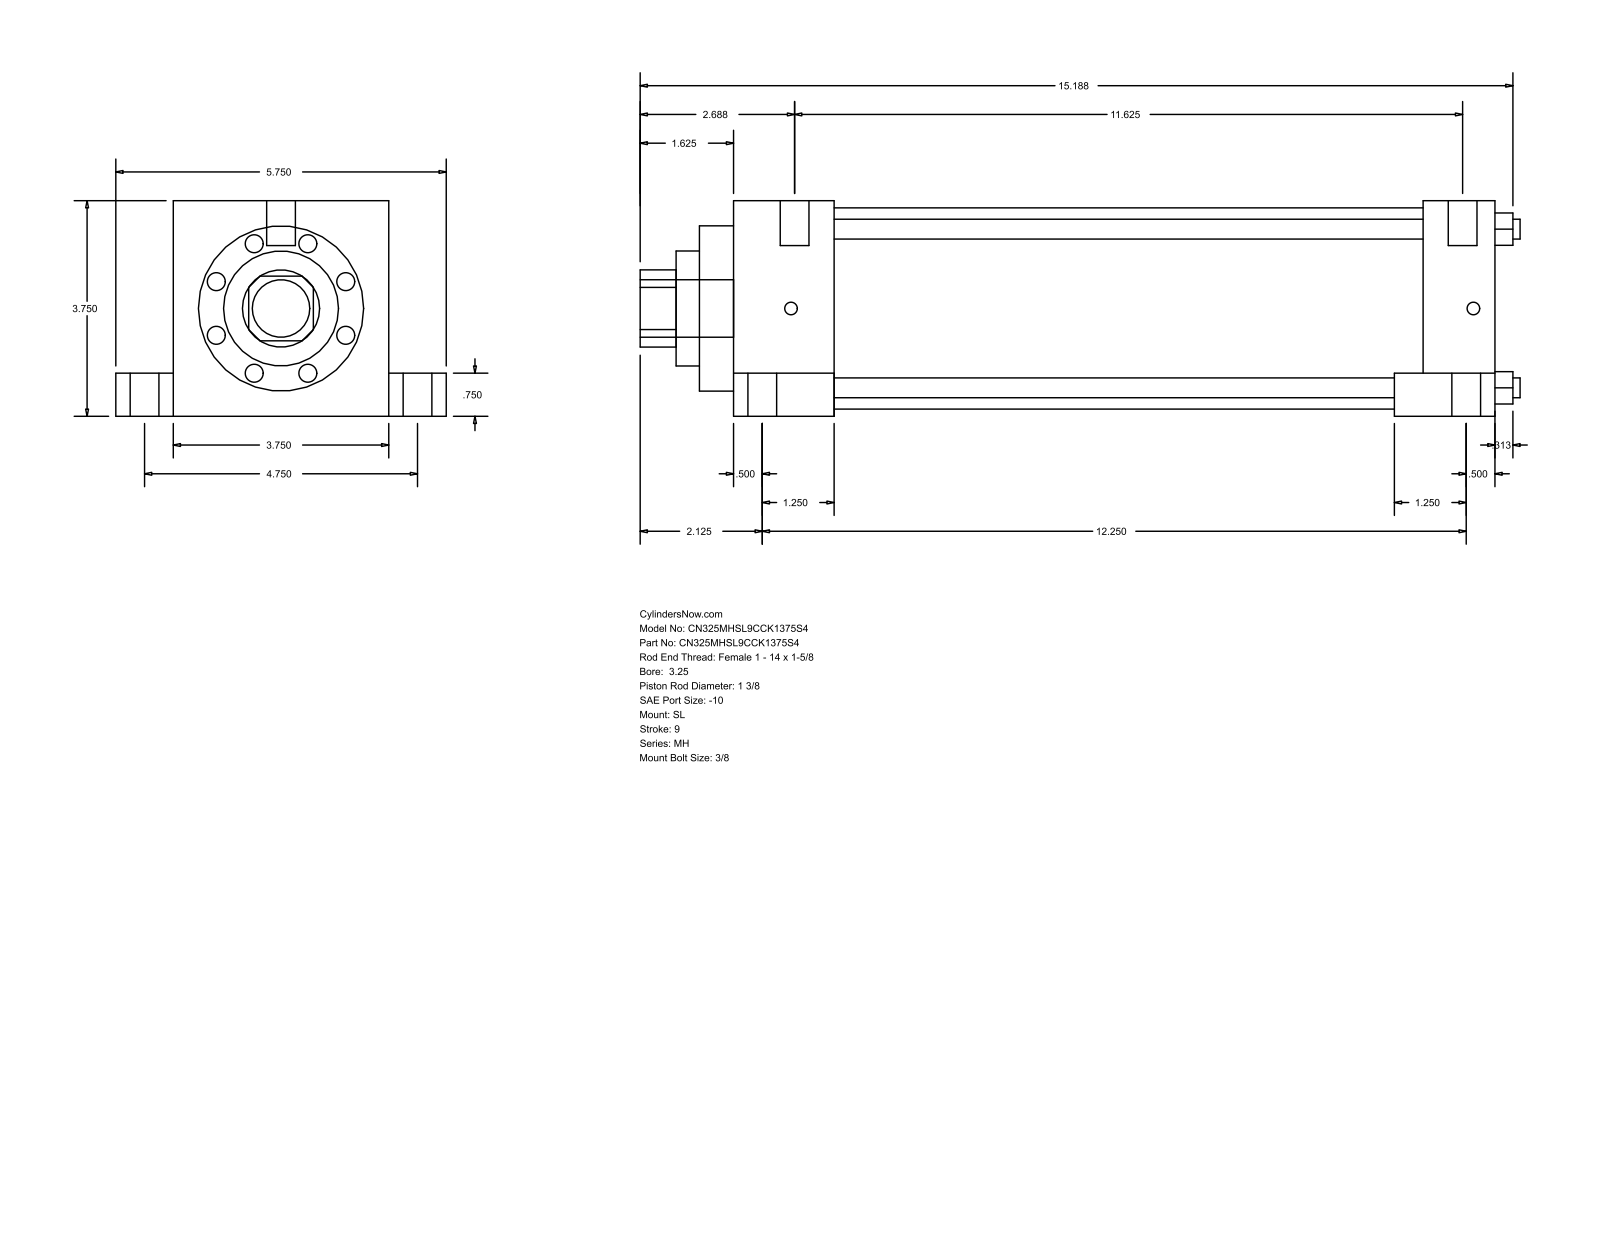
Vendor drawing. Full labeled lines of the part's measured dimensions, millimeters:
Part name (STEP PRODUCT): MH_SL__0325_1.375
STEP written by: GSSL Pune (CONFIG_CONTROL_DESIGN)
Units: millimetres
Bodies: 0 solids, 110 faces (77 planar, 33 cylindrical, 0 other)
Overall size (bounding box): 388.94 × 146.05 × 95.25
Round holes (diameter × count): ⌀8.76 ×4, ⌀34.92 ×1, ⌀50.8 ×1, ⌀73.03 ×1, ⌀88.9 ×1
Round bosses / shafts (diameter × count): ⌀12.7 ×6, ⌀19.05 ×4, ⌀5.56 ×4, ⌀25.4 ×1
Partial cylindrical surfaces — rounded edges, fillets, slot ends (radius × count): R17.06 ×1
Main face-to-face distances: 95.24, 336.55, 44.45, 292.1, 25.41, 120.65, 19.05, 76.19, 304.8, 260.35
Hole centre spacings: 49.57, 70.1, 99.14
